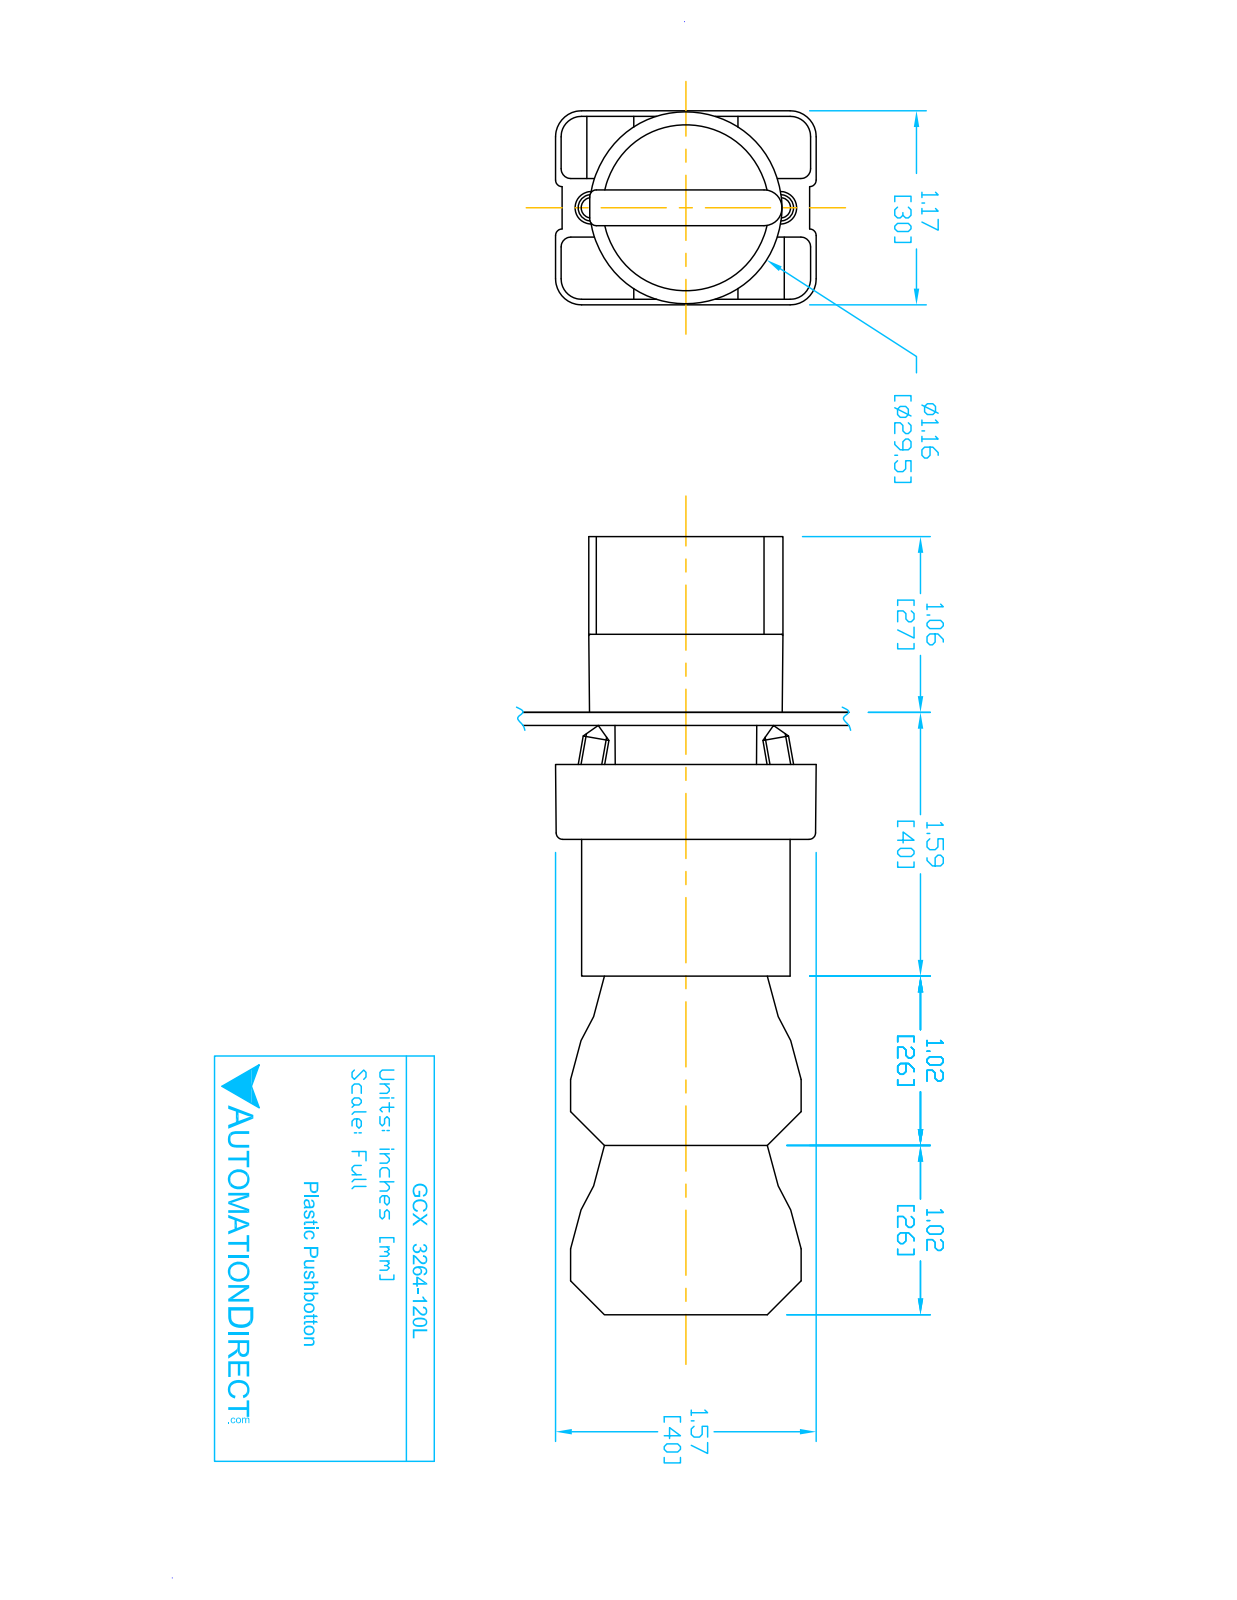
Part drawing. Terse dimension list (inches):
name: GCX3264-120L; ecx1030; ECX1050; GCX3264L OPERATOR (+2 more)
written by: SolidWorks 2016 (AUTOMOTIVE_DESIGN)
unit: in
bodies: 11 solids, 724 faces (488 planar, 193 cylindrical, 43 other)
size: 4.677 × 1.581 × 1.177
volume: 4.751 in³; area: 59.22 in²
holes: 4× ⌀0.079, 2× ⌀0.087, 2× ⌀0.124, 2× ⌀0.13, 1× ⌀0.197, 1× ⌀0.469, 1× ⌀0.878, 1× ⌀0.888, 1× ⌀1.024
bosses: 4× ⌀0.157, 1× ⌀1.175, 1× ⌀1.004, 1× ⌀0.945, 1× ⌀0.856, 1× ⌀0.78, 1× ⌀0.504
rounds: 24× R0.059, 12× R0.041, 12× R0.124, 12× R0.157, 9× R0.039, 2× R0.02, 2× R0.063, 2× R0.079
face distances: 0.579, 0.593, 1.024, 1.171, 0.014, 0.827, 1.85, 3.043, 2.02, 1.193
hole spacings: 0.236, 1.003, 0.974, 0.472, 0.539, 0.544, 1.083, 0.484
